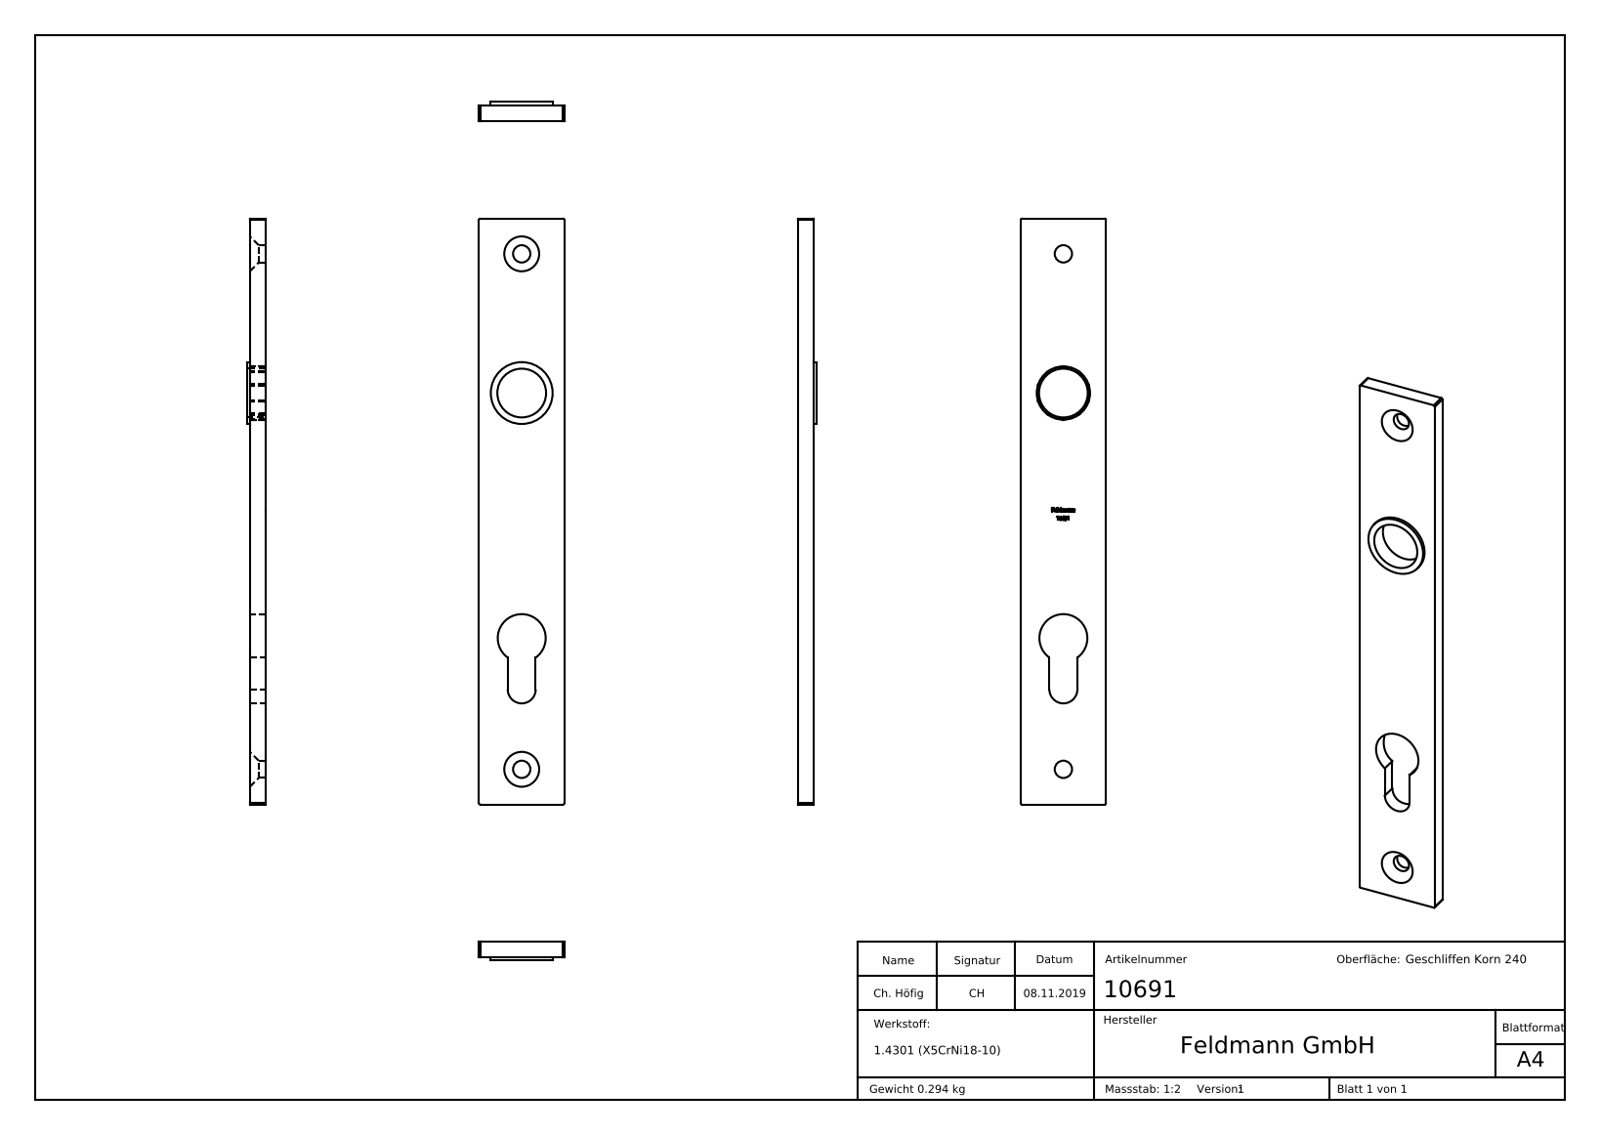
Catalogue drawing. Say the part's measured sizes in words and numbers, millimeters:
The part is named "1069X Teil2; 1069X Teil1_10691 Teil1; 1069X Teil2_1069X Teil2; 10691 (+1 more)". Its 3-D file was written by "SolidWorks 2015 (CONFIG_CONTROL_DESIGN)". It is 2 solids with 240 faces: 122 planar, 31 cylindrical and 87 other. Overall it measures 220 by 32 by 7.2 millimeters. Its volume is 37 596 cubic millimeters and its surface area 17 800 square millimeters. Round holes: 2 of diameter 6.5, 1 of diameter 18, 1 of diameter 18.3. Round bosses or shafts: 1 of diameter 23.2, 1 of diameter 20, 1 of diameter 19.5. Partial cylindrical surfaces (rounded edges, fillets, slot ends): 4 of radius 0.5, 1 of radius 5.25. The main face-to-face distances are 6, 32, 220, 1.2, 7.2, 10.75, 21.25, 10.5, 5.8, 7. The hole center spacings are 49.25, 52.25, 92, 141.25, 144.25, 193.5.
